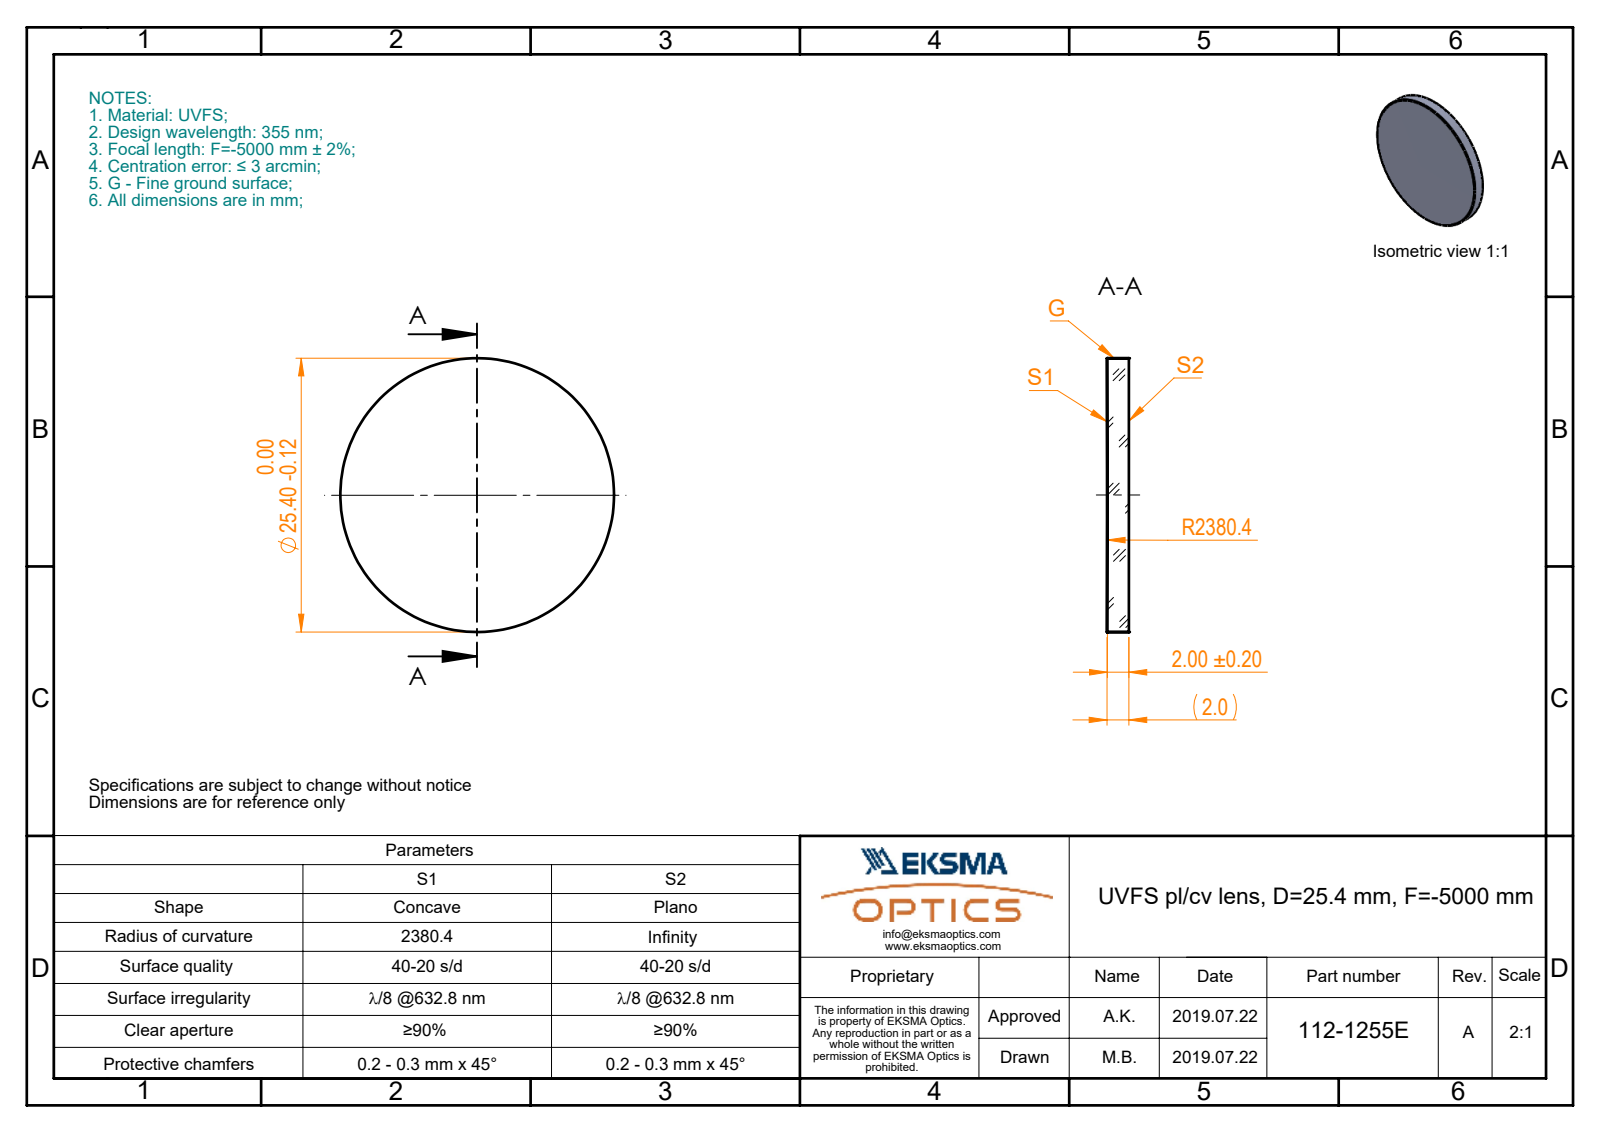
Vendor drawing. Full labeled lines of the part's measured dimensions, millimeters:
Part name (STEP PRODUCT): 112-1255E UVFS pl-cv 25.4 F-5000
STEP written by: SolidWorks 2017 (CONFIG_CONTROL_DESIGN)
Units: millimetres
Bodies: 1 solid, 5 faces (1 planar, 2 cylindrical, 2 other)
Overall size (bounding box): 25.4 × 25.4 × 2.03
Volume: 1 022 mm³ · Surface area: 1 176 mm²
Round bosses / shafts (diameter × count): ⌀25.4 ×1
